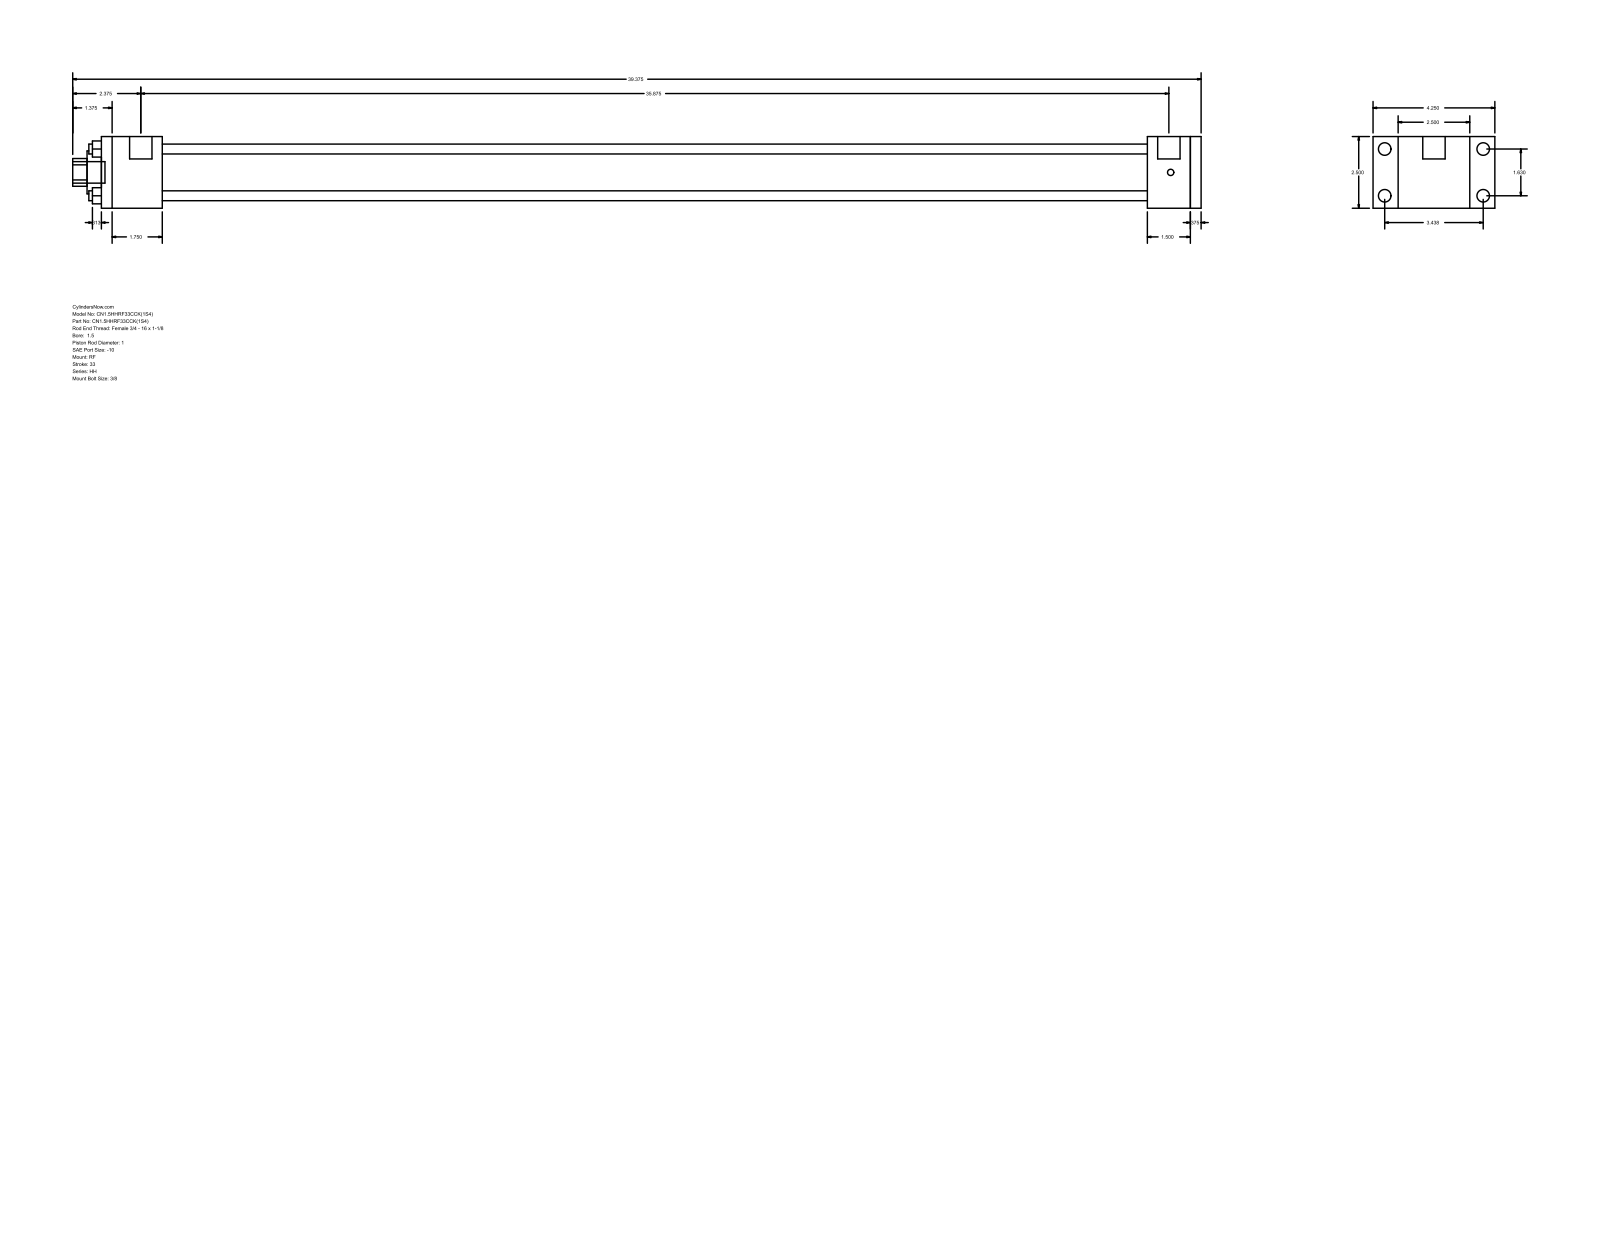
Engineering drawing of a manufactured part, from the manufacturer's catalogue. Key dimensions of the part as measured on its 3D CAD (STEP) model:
Part name (STEP PRODUCT): HH_RF__0150_1
STEP written by: GSSL Pune (CONFIG_CONTROL_DESIGN)
Units: millimetres
Bodies: 0 solids, 92 faces (64 planar, 28 cylindrical, 0 other)
Overall size (bounding box): 1000.12 × 107.95 × 63.5
Round holes (diameter × count): ⌀8.76 ×4, ⌀25.4 ×1, ⌀38.1 ×1, ⌀44.45 ×1
Round bosses / shafts (diameter × count): ⌀11.13 ×4, ⌀5.56 ×4, ⌀19.84 ×2, ⌀19.05 ×1
Partial cylindrical surfaces — rounded edges, fillets, slot ends (radius × count): R12.29 ×1
Main face-to-face distances: 63.5, 9.52, 873.12, 911.22, 920.74, 38.1, 47.62, 53.98, 927.1, 965.2
Hole centre spacings: 29.27, 41.4, 58.55
